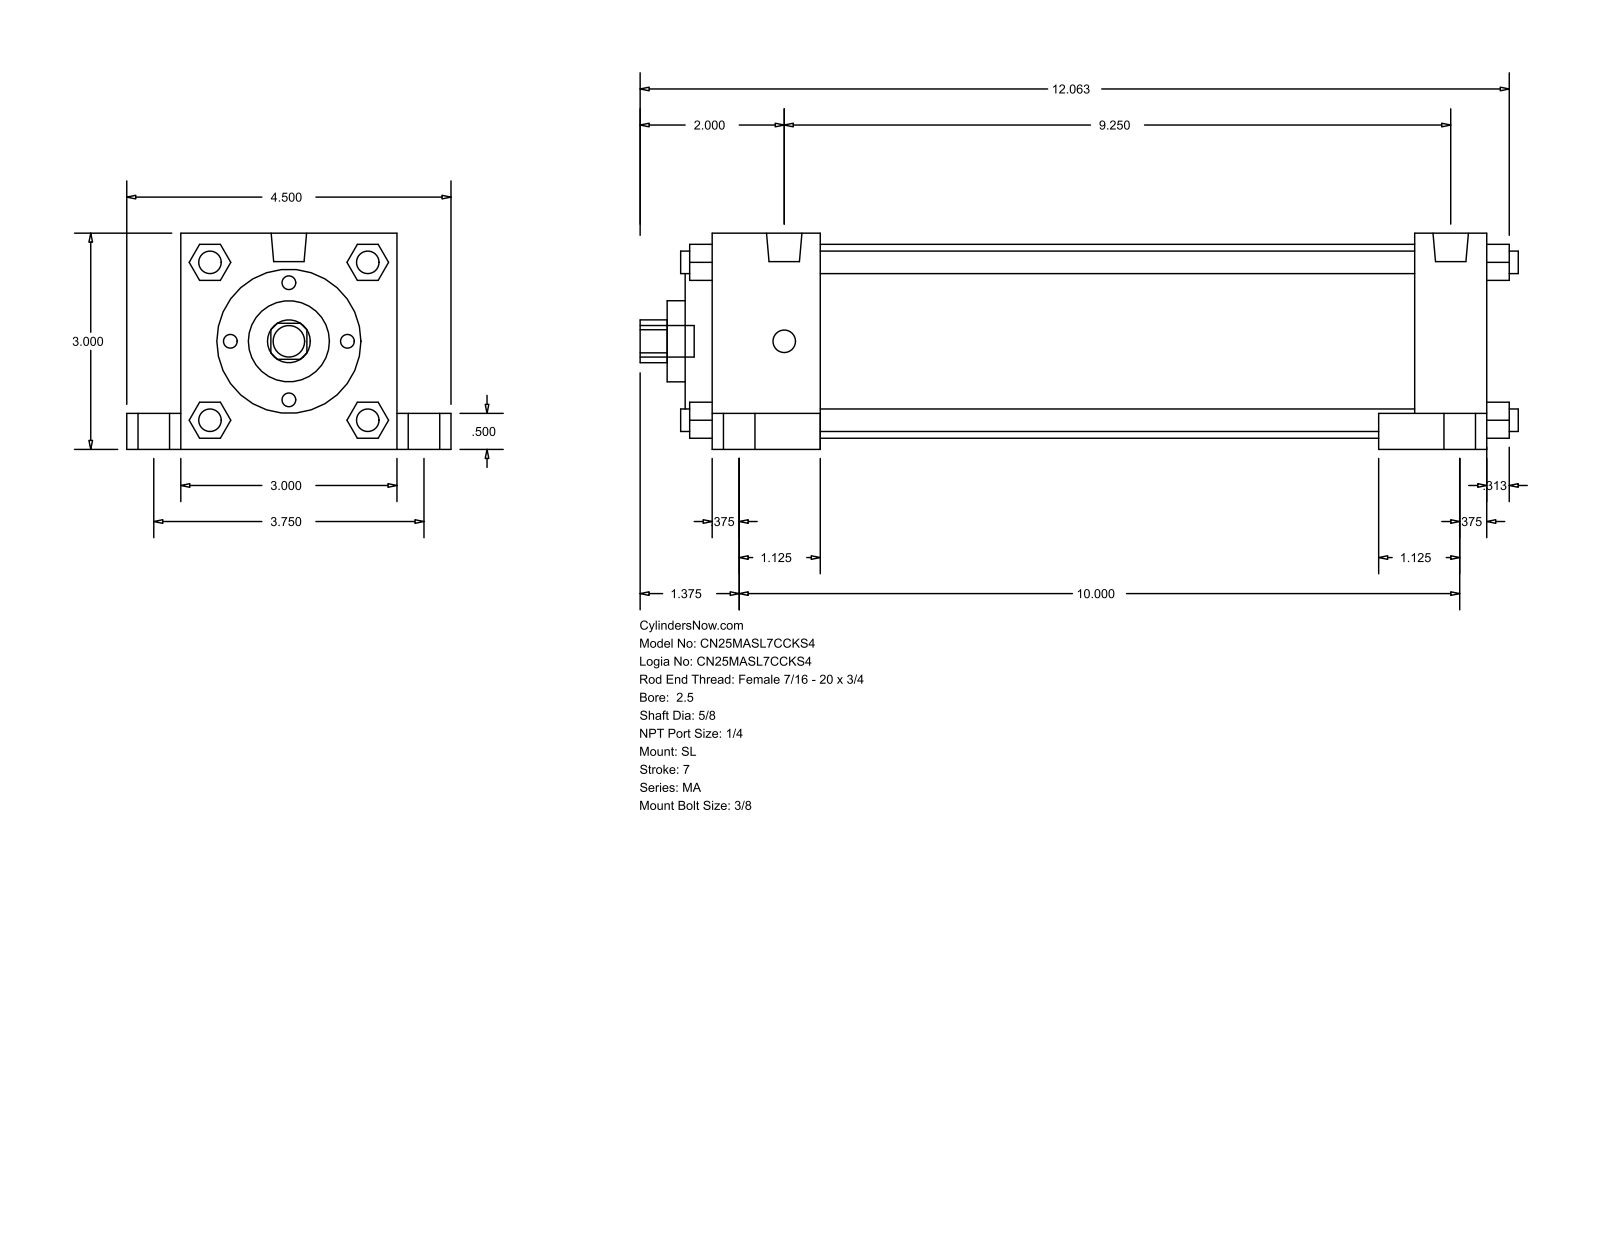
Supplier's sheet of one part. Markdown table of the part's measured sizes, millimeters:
| quantity | value |
| --- | --- |
| part name | MA_SL__0250_0.625 |
| STEP written by | GSSL Pune (CONFIG_CONTROL_DESIGN) |
| units | millimeters |
| bodies | 0 solids, 150 faces (113 planar, 37 cylindrical, 0 other) |
| overall size | 309.56 × 114.3 × 76.2 |
| round holes (diameter × count) | 15.88 × 1, 28.57 × 1, 50.8 × 1, 68.33 × 1 |
| round bosses / shafts (diameter × count) | 7.94 × 8, 11.11 × 5, 17.46 × 4, 12.49 × 2 |
| partial cylindrical surfaces (radius × count) | 7.54 × 1 |
| main face-to-face distances | 76.2, 273.05, 12.7, 209.55, 25.4, 38.1, 234.95, 247.65, 19.05, 63.5 |
